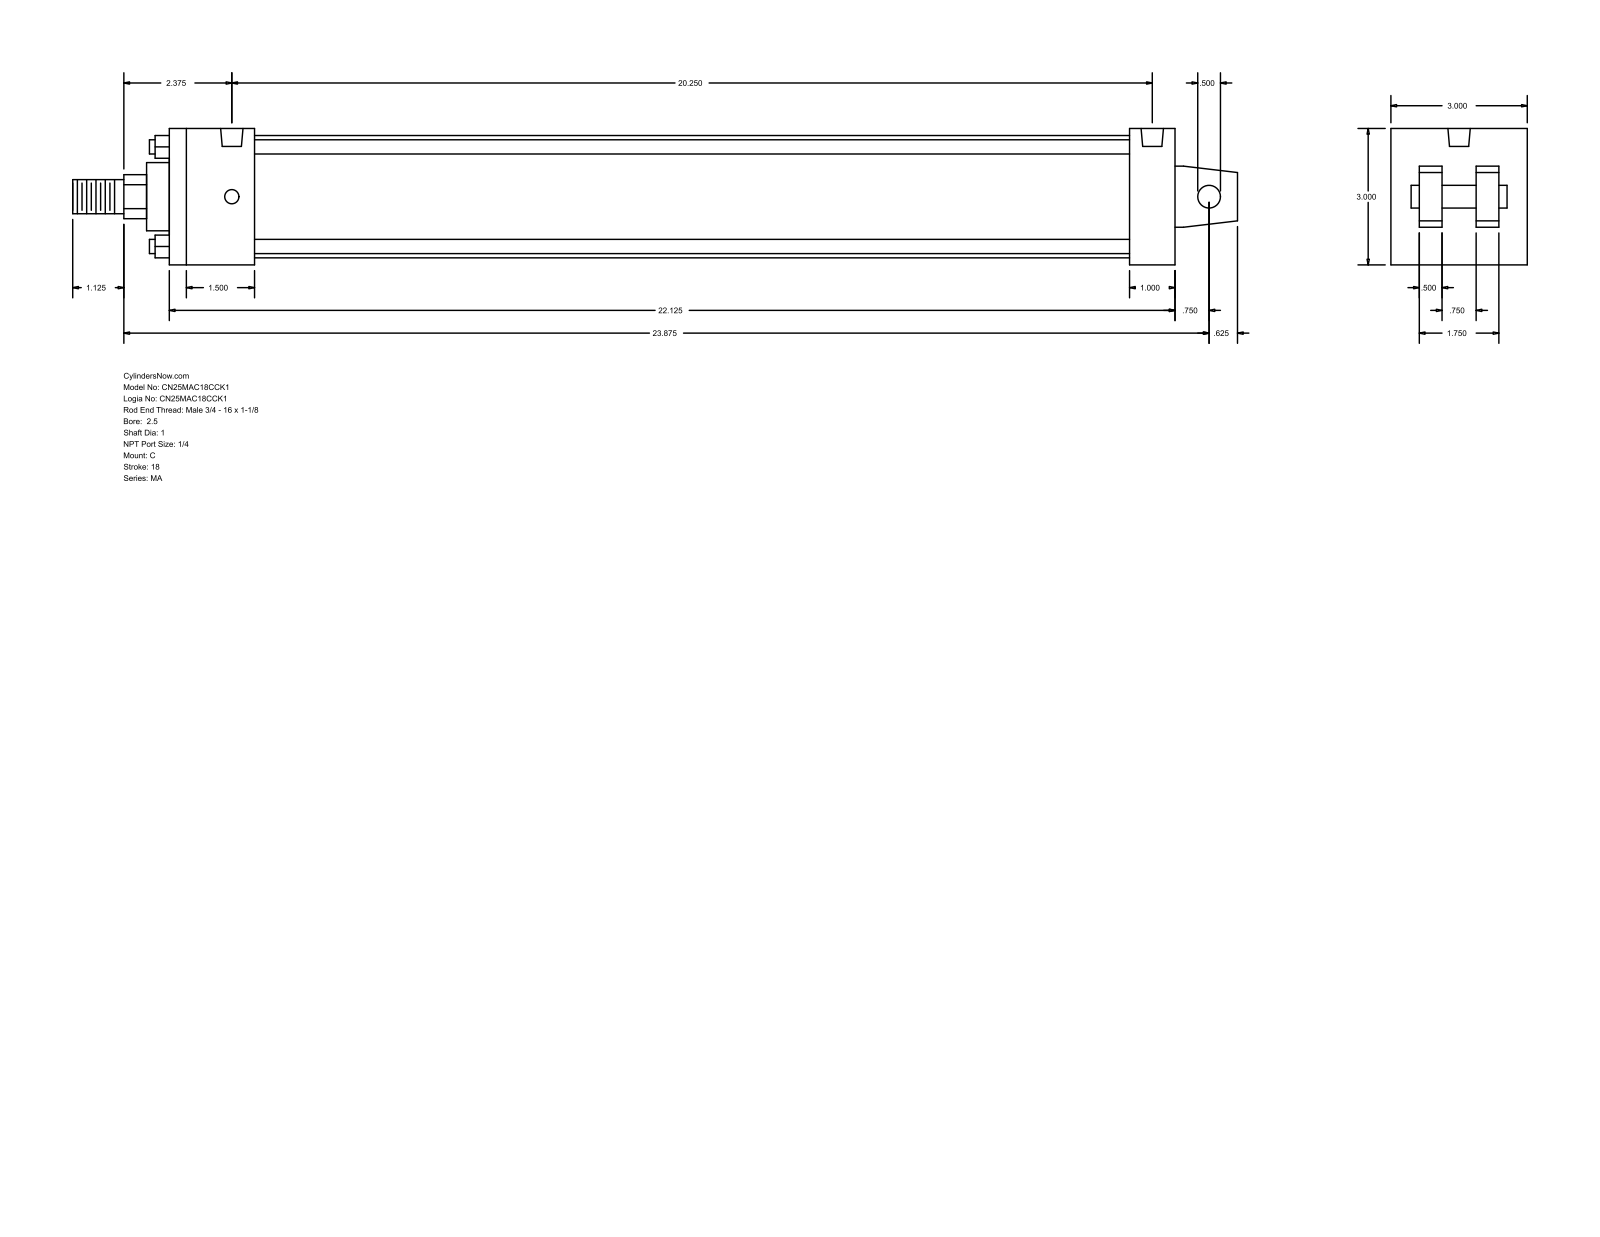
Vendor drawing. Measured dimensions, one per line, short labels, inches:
name: MA_C__0250_1
written by: GSSL Pune (CONFIG_CONTROL_DESIGN)
unit: in
bodies: 0 solids, 103 faces (76 planar, 27 cylindrical, 0 other)
size: 25.625 × 3 × 3
holes: 4× ⌀0.313, 2× ⌀0.492
bosses: 4× ⌀0.313, 1× ⌀2.69, 1× ⌀1.5, 1× ⌀1, 1× ⌀0.75, 1× ⌀0.5
rounds: 1× R0.484
face distances: 3, 22.125, 1.875, 0.5, 2.375, 0.625, 1, 1.125, 21.125, 19.25
hole spacings: 20.25
